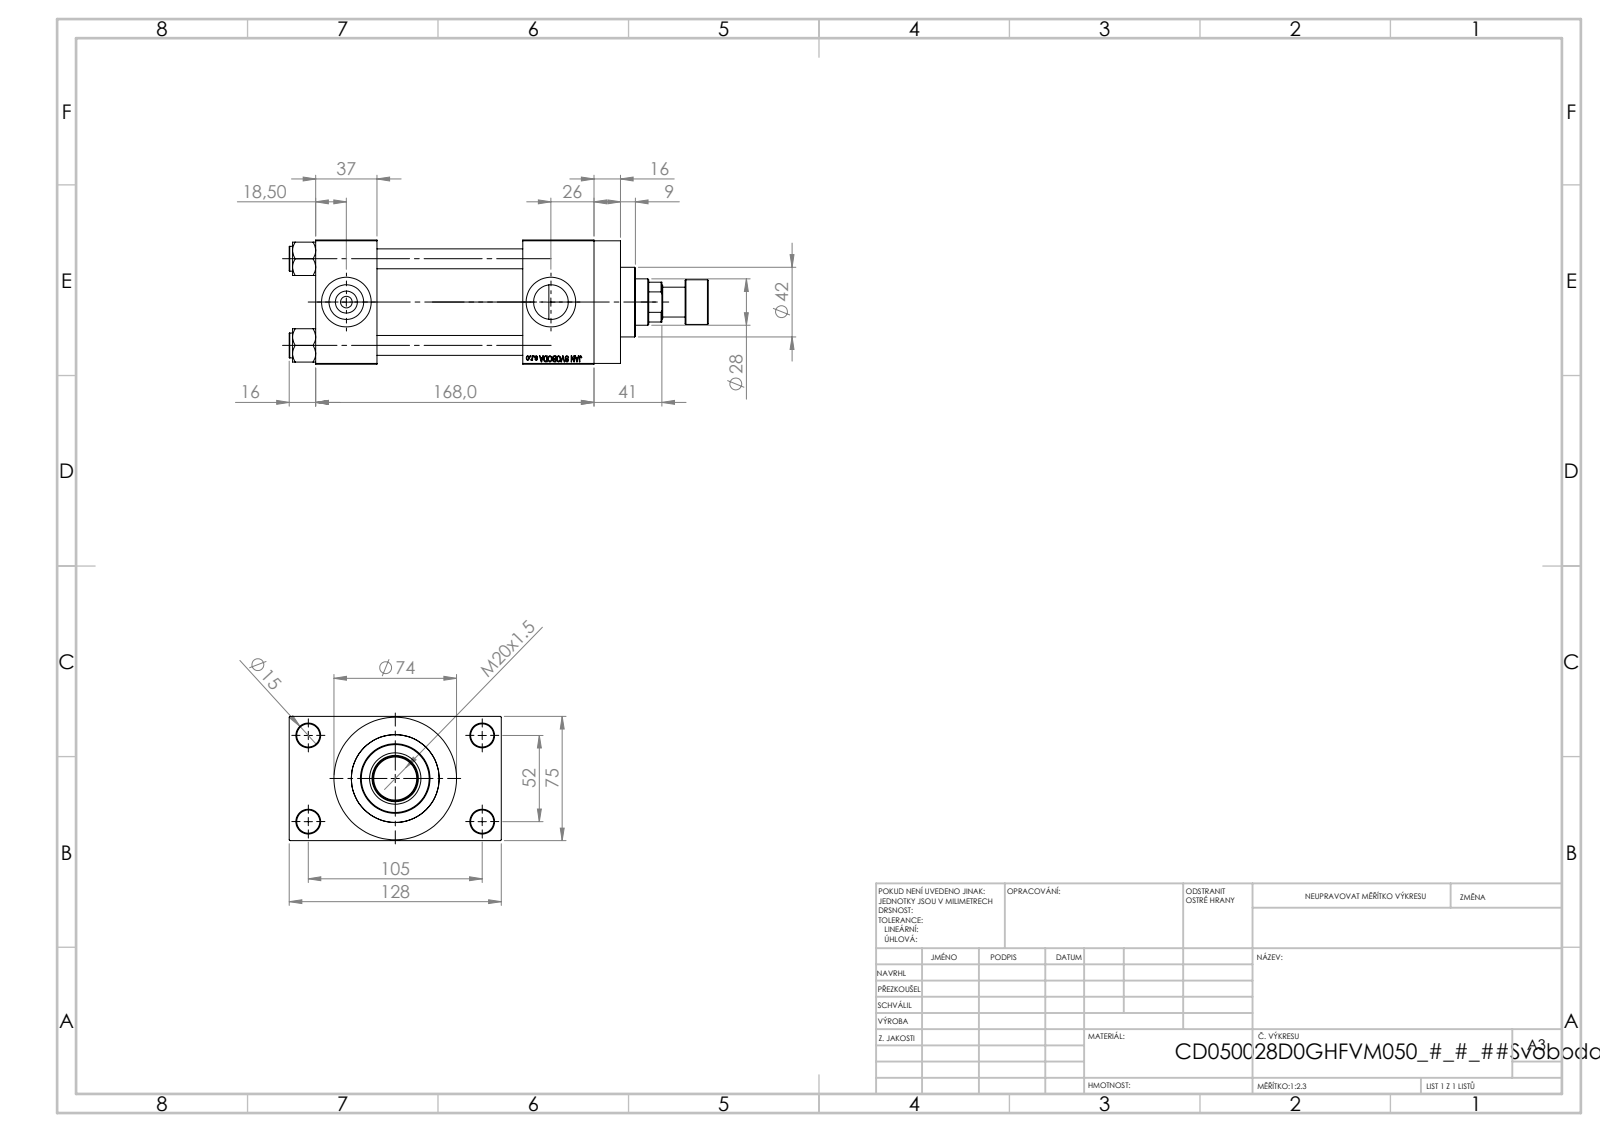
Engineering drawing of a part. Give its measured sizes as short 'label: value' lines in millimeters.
name: V215CD_VCP_D; V215CD_D_Body; V215CR_ROD_END_F; V215CD_NUT_M5_D (+2 more)
written by: SolidWorks 2019 (CONFIG_CONTROL_DESIGN)
unit: mm
bodies: 12 solids, 1117 faces (501 planar, 92 cylindrical, 524 other)
size: 253 × 128 × 75
volume: 864 846 mm³; area: 191 018 mm²
holes: 4× ⌀12, 4× ⌀14, 2× ⌀7, 2× ⌀20.96, 2× ⌀30, 1× ⌀18.5, 1× ⌀28, 1× ⌀31, 1× ⌀41, 1× ⌀50, 1× ⌀53
bosses: 4× ⌀15, 1× ⌀74, 1× ⌀56, 1× ⌀42, 1× ⌀27, 1× ⌀18
face distances: 75, 88, 125, 37, 26.5, 168, 131, 43, 101.5, 16
hole spacings: 26.35, 36.98, 52.3, 58.43, 58.59, 78.65, 94.37, 52
